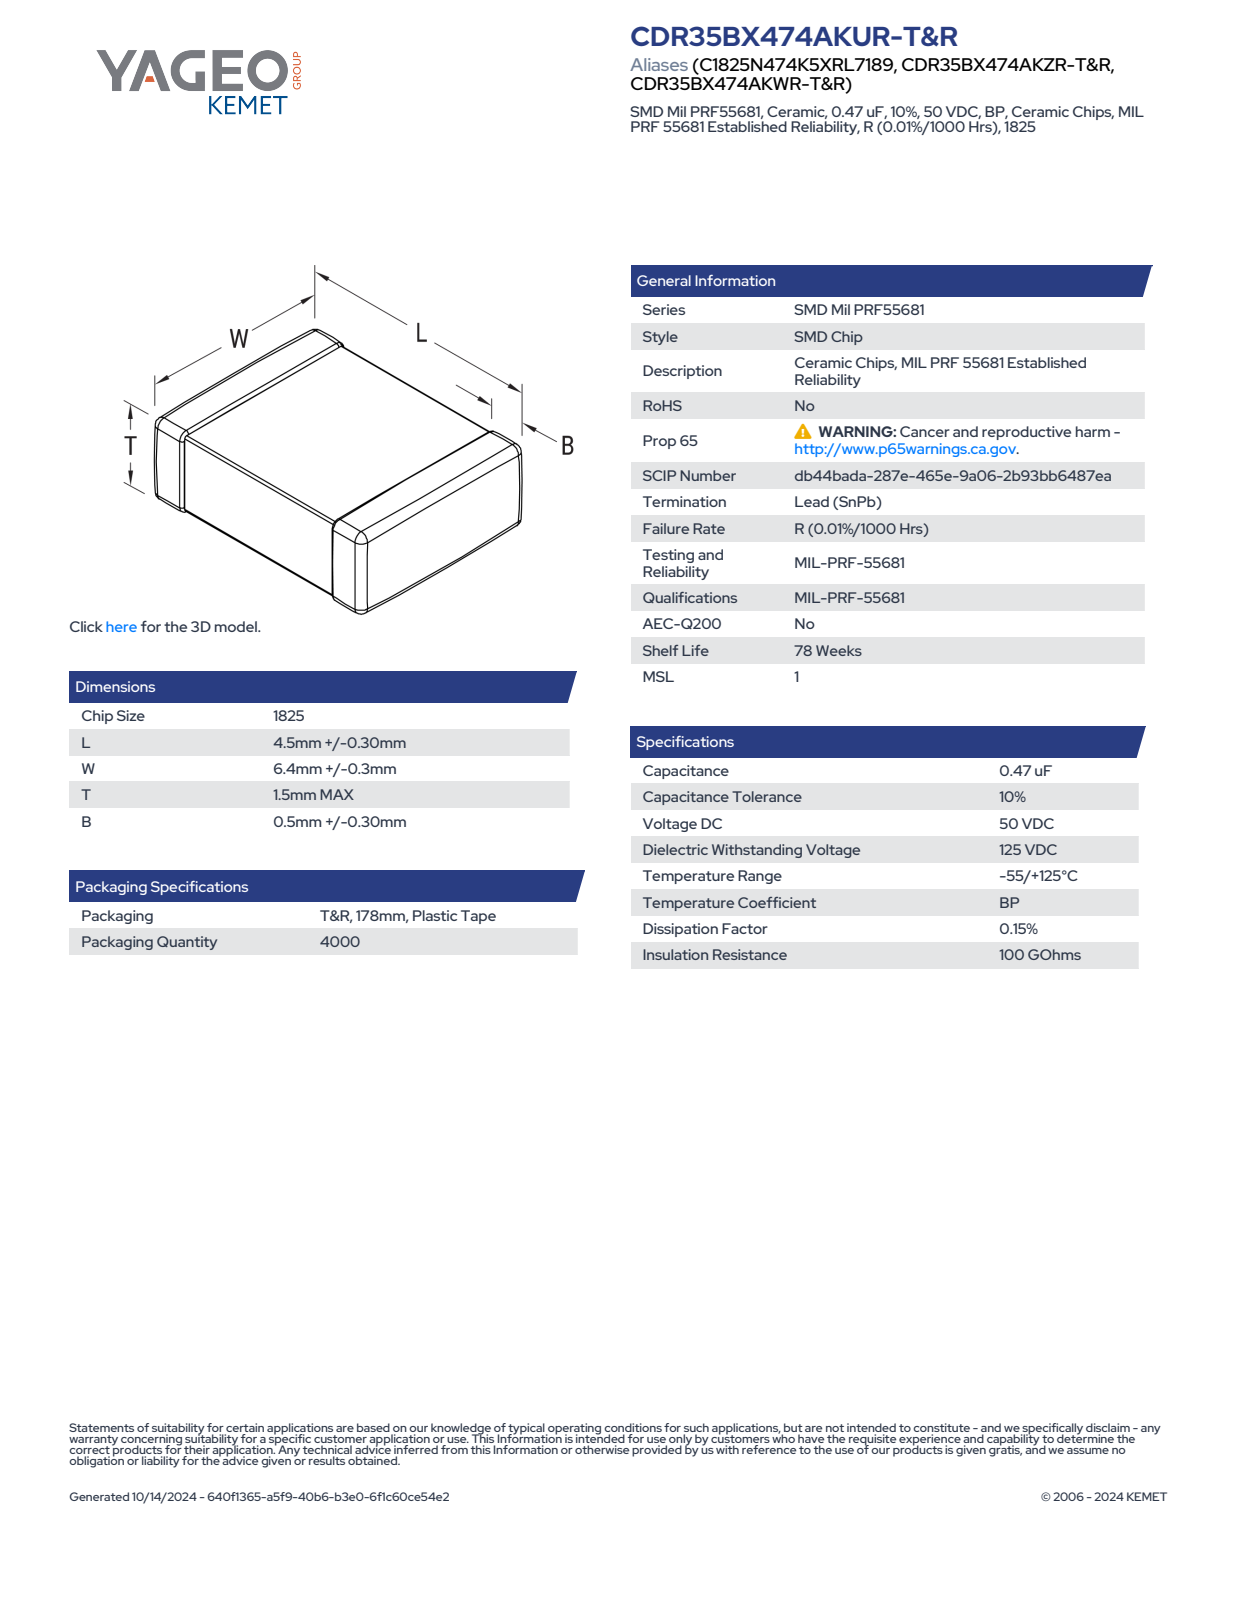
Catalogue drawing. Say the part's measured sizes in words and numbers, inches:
The part is named "CCS_STDNOS_1825_L4.8W6.7T1.5B0.8". Its 3-D file was written by "SolidWorks 2021 (AUTOMOTIVE_DESIGN)". It is 4 solids with 125 faces: 71 planar, 38 cylindrical and 16 other. Overall it measures 0.264 by 0.189 by 0.059 inches. Its volume is 0.003 cubic inches and its surface area 0.15 square inches. Partial cylindrical surfaces (rounded edges, fillets, slot ends): 24 of radius 0.006. The main face-to-face distances are 0.048, 0.054, 0.189, 0.059, 0.253, 0.258, 0.264, 0.054, 0.048, 0.013.
